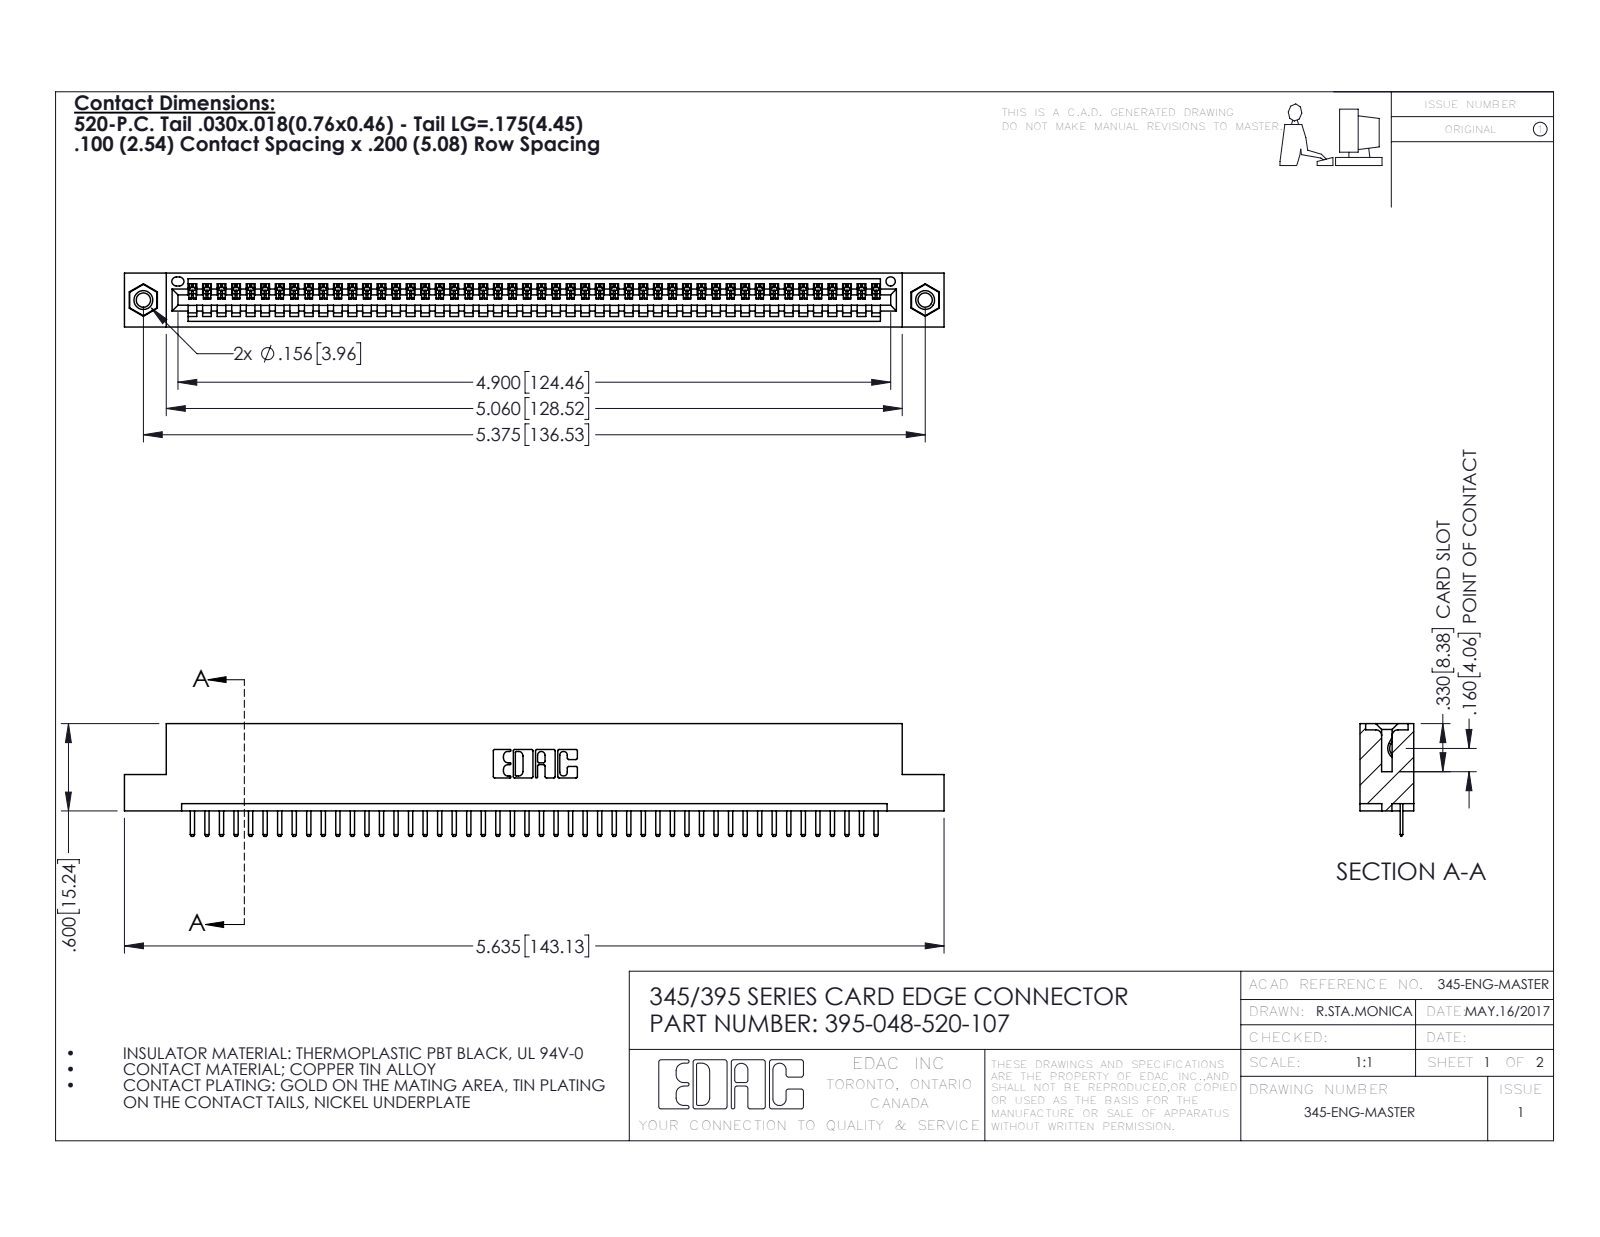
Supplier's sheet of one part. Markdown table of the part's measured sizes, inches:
| quantity | value |
| --- | --- |
| part name | 345-292-001_345-293-120; 345 Part_Flush Mounting Lugs - 0.156 Dia-TI; 395-048-520-107; 345-250-001_345-250-005-103 |
| STEP written by | SolidWorks 2016 (CONFIG_CONTROL_DESIGN) |
| units | inches |
| bodies | 51 solids, 3162 faces (2128 planar, 1018 cylindrical, 16 other) |
| overall size | 5.635 × 0.775 × 0.37 |
| volume | 0.823 in³ |
| surface area | 27.27 in² |
| round holes (diameter × count) | 0.098 × 2, 0.125 × 2, 0.156 × 2, 0.064 × 1 |
| round bosses / shafts (diameter × count) | 0.155 × 2 |
| partial cylindrical surfaces (radius × count) | 0.01 × 98, 0.006 × 96, 0.01 × 22, 0.007 × 6, 0.031 × 6, 0.026 × 3, 0.031 × 2, 0.04 × 2 |
| main face-to-face distances | 0.072, 0.298, 0.37, 0.2, 0.098, 0.272, 0.025, 0.225, 0.072, 0.149 |
| hole center spacings | 0.27, 5.139, 5.375 |
